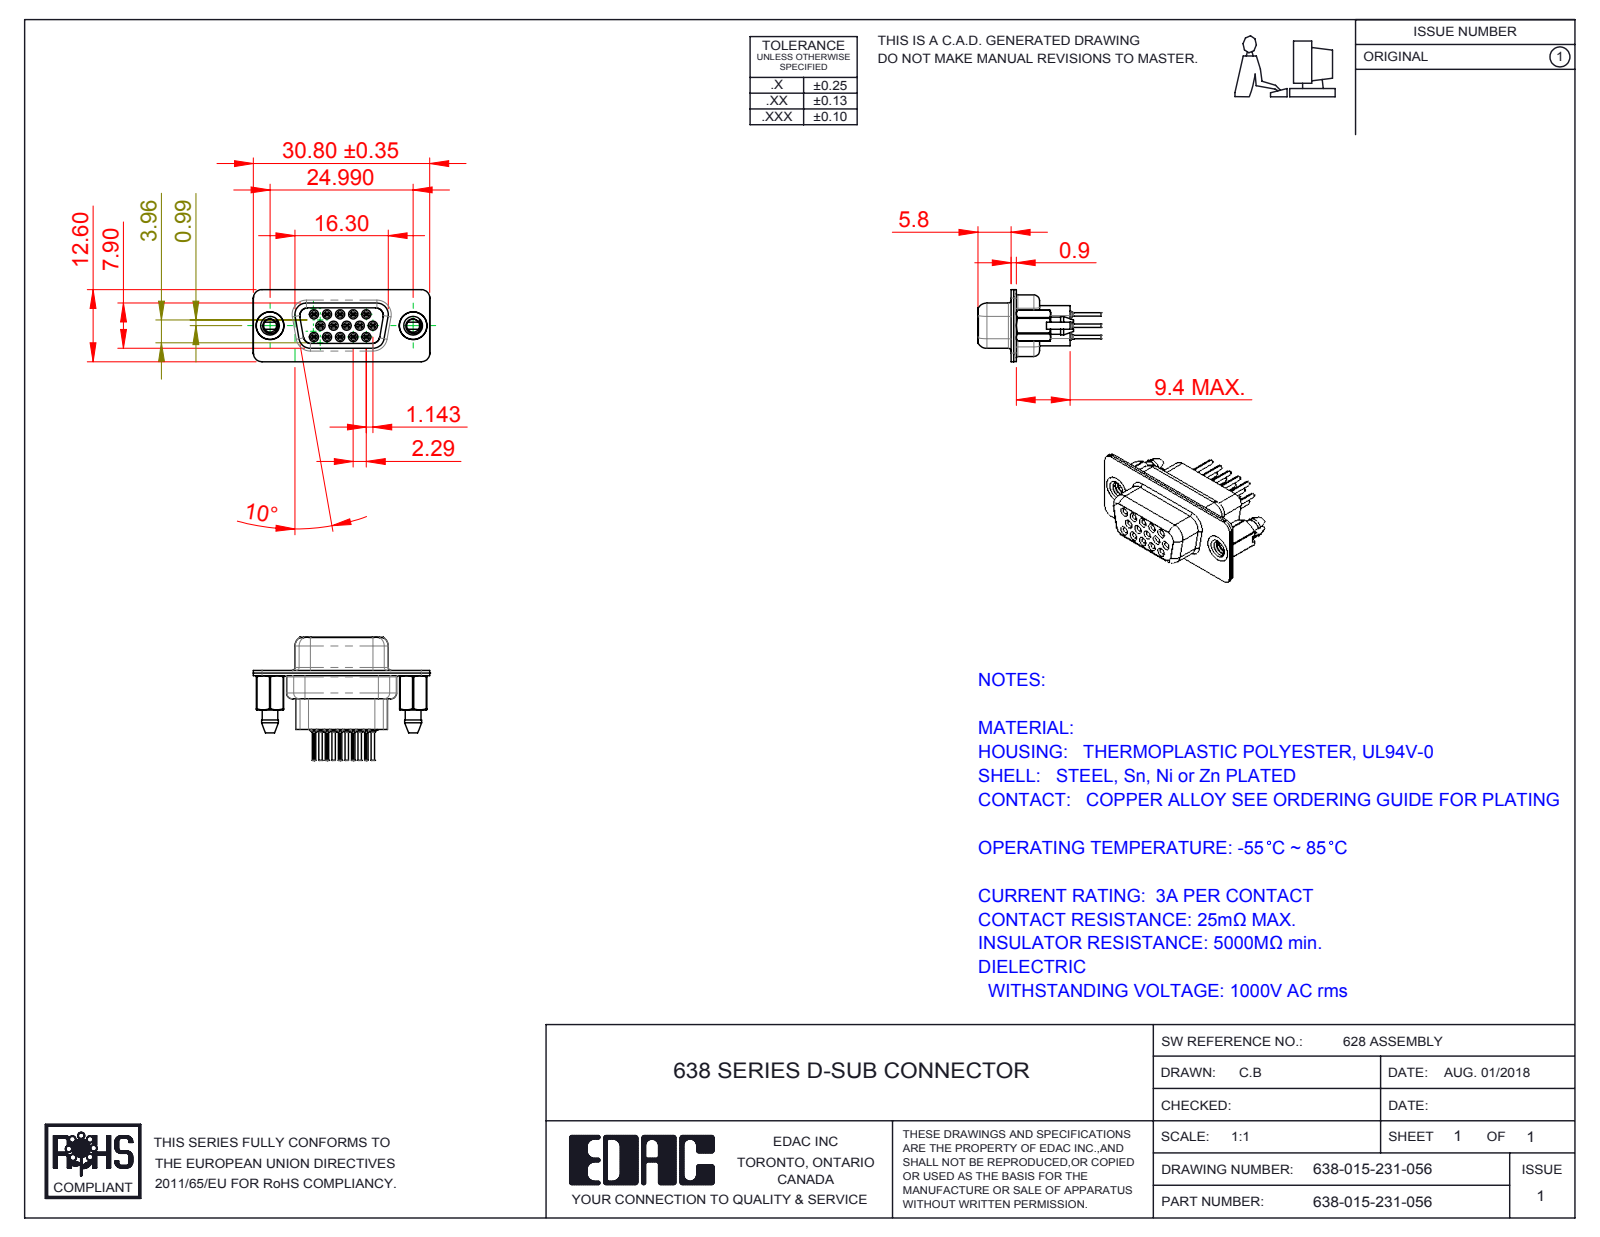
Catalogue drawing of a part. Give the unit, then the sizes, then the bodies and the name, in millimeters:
Units: millimetres
Overall size (bounding box): 30.81 × 21.5 × 12.6
Round holes (diameter × count): ⌀0.2 ×15, ⌀0.8 ×15, ⌀1 ×15, ⌀1.1 ×15, ⌀1.6 ×15, ⌀1.7 ×15, ⌀1.8 ×15, ⌀2 ×2, ⌀2.26 ×2, ⌀4 ×2, ⌀4.05 ×2, ⌀4.85 ×2
Round bosses / shafts (diameter × count): ⌀2 ×15, ⌀1.5 ×15, ⌀1.2 ×15, ⌀0.6 ×15, ⌀4.95 ×2, ⌀4.8 ×2
Partial cylindrical surfaces — rounded edges, fillets, slot ends (radius × count): R0.1 ×30, R1.5 ×22, R2 ×12, R0.28 ×10, R1.55 ×8, R1.35 ×5, R0.25 ×4, R0.5 ×4
Main face-to-face distances: 0.45, 0.9, 0.4, 1.43, 6.6, 8.88, 7, 2.28, 5.8, 9.4
Hole centre spacings: 3.96, 2.28, 4.57, 2.29, 6.05, 6.04, 6.86, 7.92
Volume: 1 996 mm³ · Surface area: 6 817 mm²
Bodies: 20 solids, 2198 faces (564 planar, 664 cylindrical, 970 other)
Part name (STEP PRODUCT): 638-015-231-056; 638 Housing_15 Contacts HP; 638 Shell Front_15 Contacts; 638 4-40 Threaded Boardlock_LP (+4 more)
STEP written by: SolidWorks 2016 (CONFIG_CONTROL_DESIGN)
